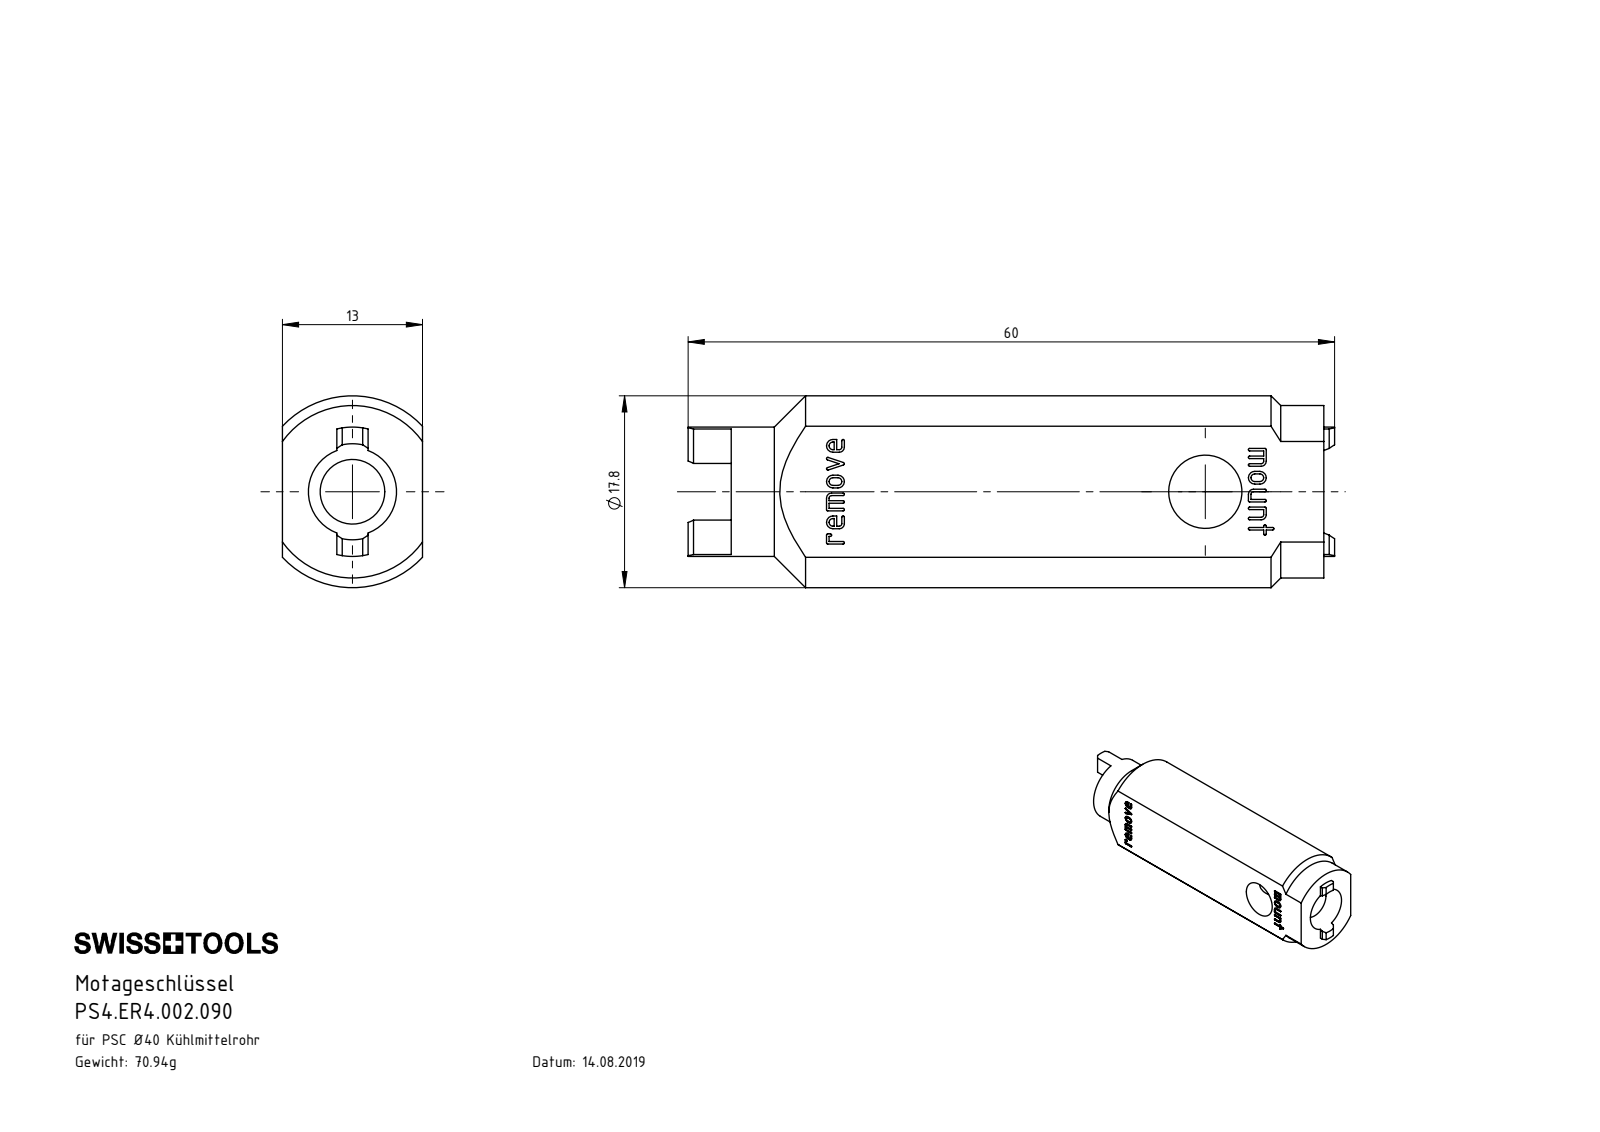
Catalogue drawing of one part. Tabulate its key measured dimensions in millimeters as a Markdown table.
| quantity | value |
| --- | --- |
| part name | PS4.ER4.002.090 |
| STEP written by | SolidWorks 2017 (AUTOMOTIVE_DESIGN) |
| units | millimeters |
| bodies | 1 solid, 214 faces (114 planar, 10 cylindrical, 90 other) |
| overall size | 60 × 17.8 × 13 |
| volume | 9 037 mm³ |
| surface area | 4 304 mm² |
| round holes (diameter × count) | 6 × 1, 6.8 × 1 |
| round bosses / shafts (diameter × count) | 12 × 1 |
| partial cylindrical surfaces (radius × count) | 8 × 1, 8.9 × 1 |
| main face-to-face distances | 13, 55, 5.05, 7.95, 2.9, 59, 4, 5.04, 7.94, 12.99 |
